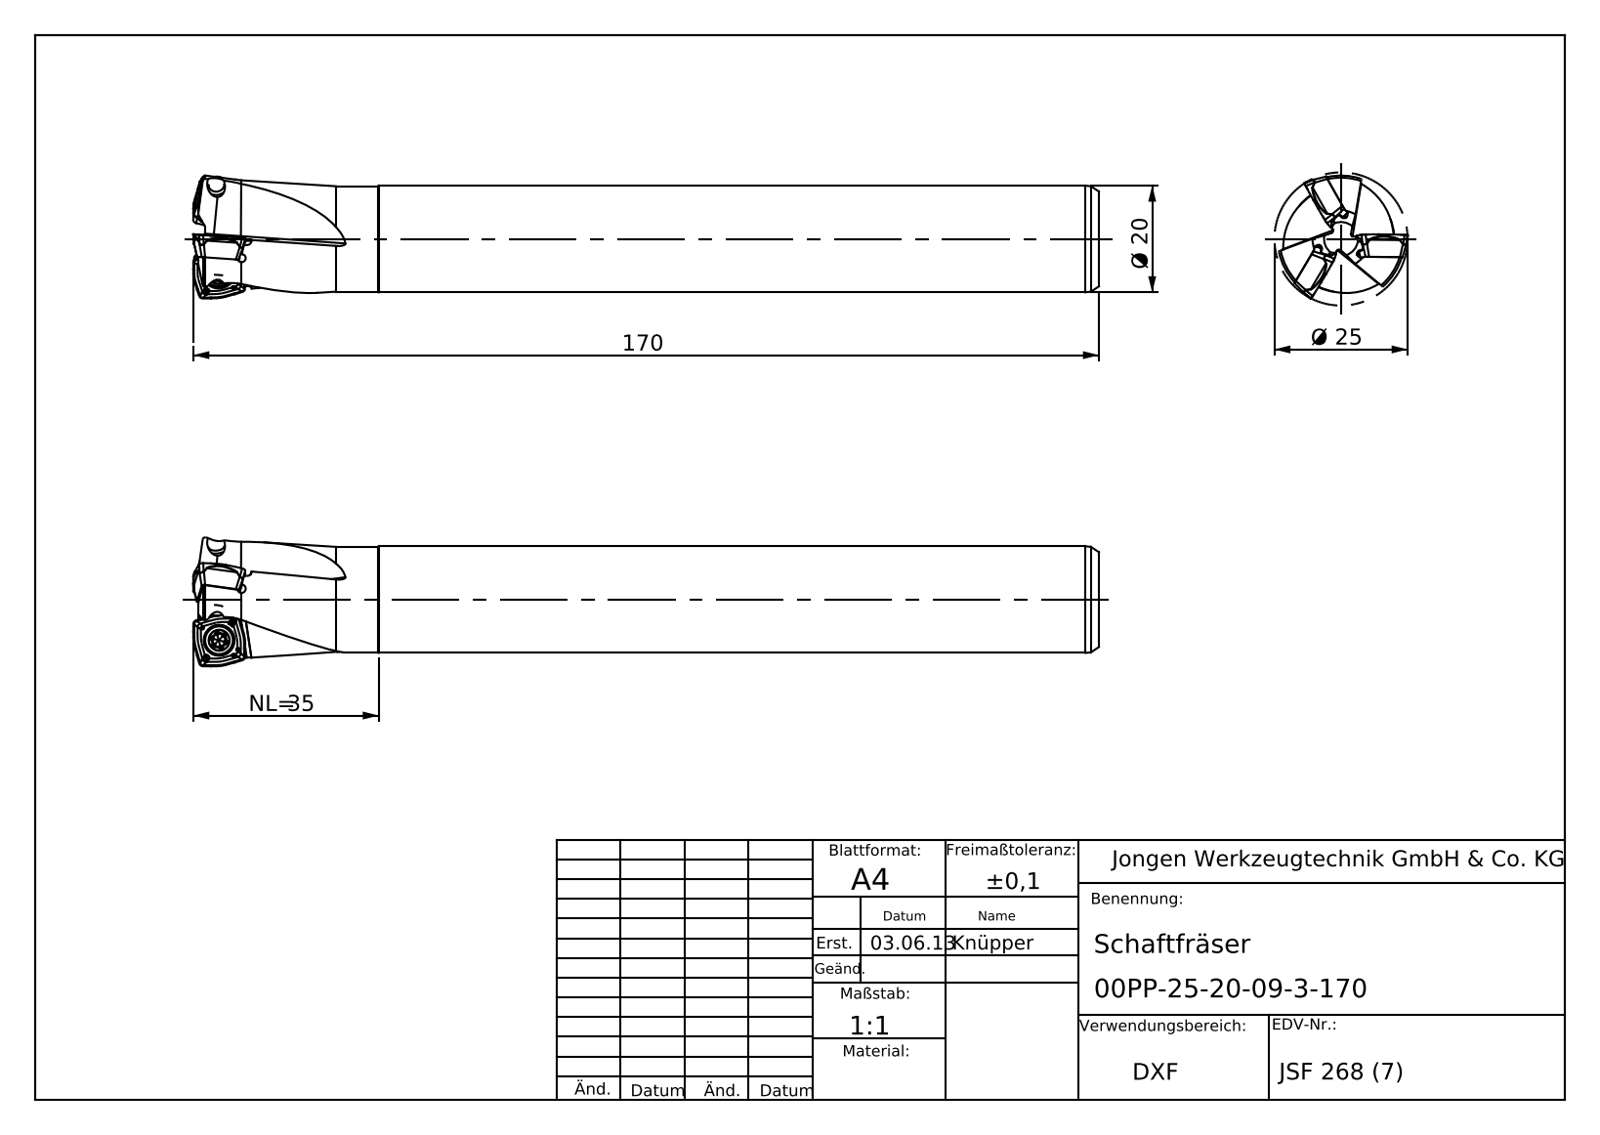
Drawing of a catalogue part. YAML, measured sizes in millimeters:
part_name: "00PP-25-20-09-3-170"
step_written_by: "SolidWorks 2013 (AUTOMOTIVE_DESIGN)"
units: millimeters
bodies: {solids: 1, faces: 68, planar: 29, cylindrical: 20, other: 19}
overall_size: [169.98, 25.03, 25.03]
volume: 53791
surface_area: 12132
round_bosses_or_shafts:
  - {diameter: 20, count: 1}
  - {diameter: 19.8, count: 1}
partial_cylinders:
  - {radius: 0.5, count: 6}
  - {radius: 0.8, count: 6}
  - {radius: 0.75, count: 3}
  - {radius: 2, count: 3}
face_to_face_distances: [167.8, 1]
